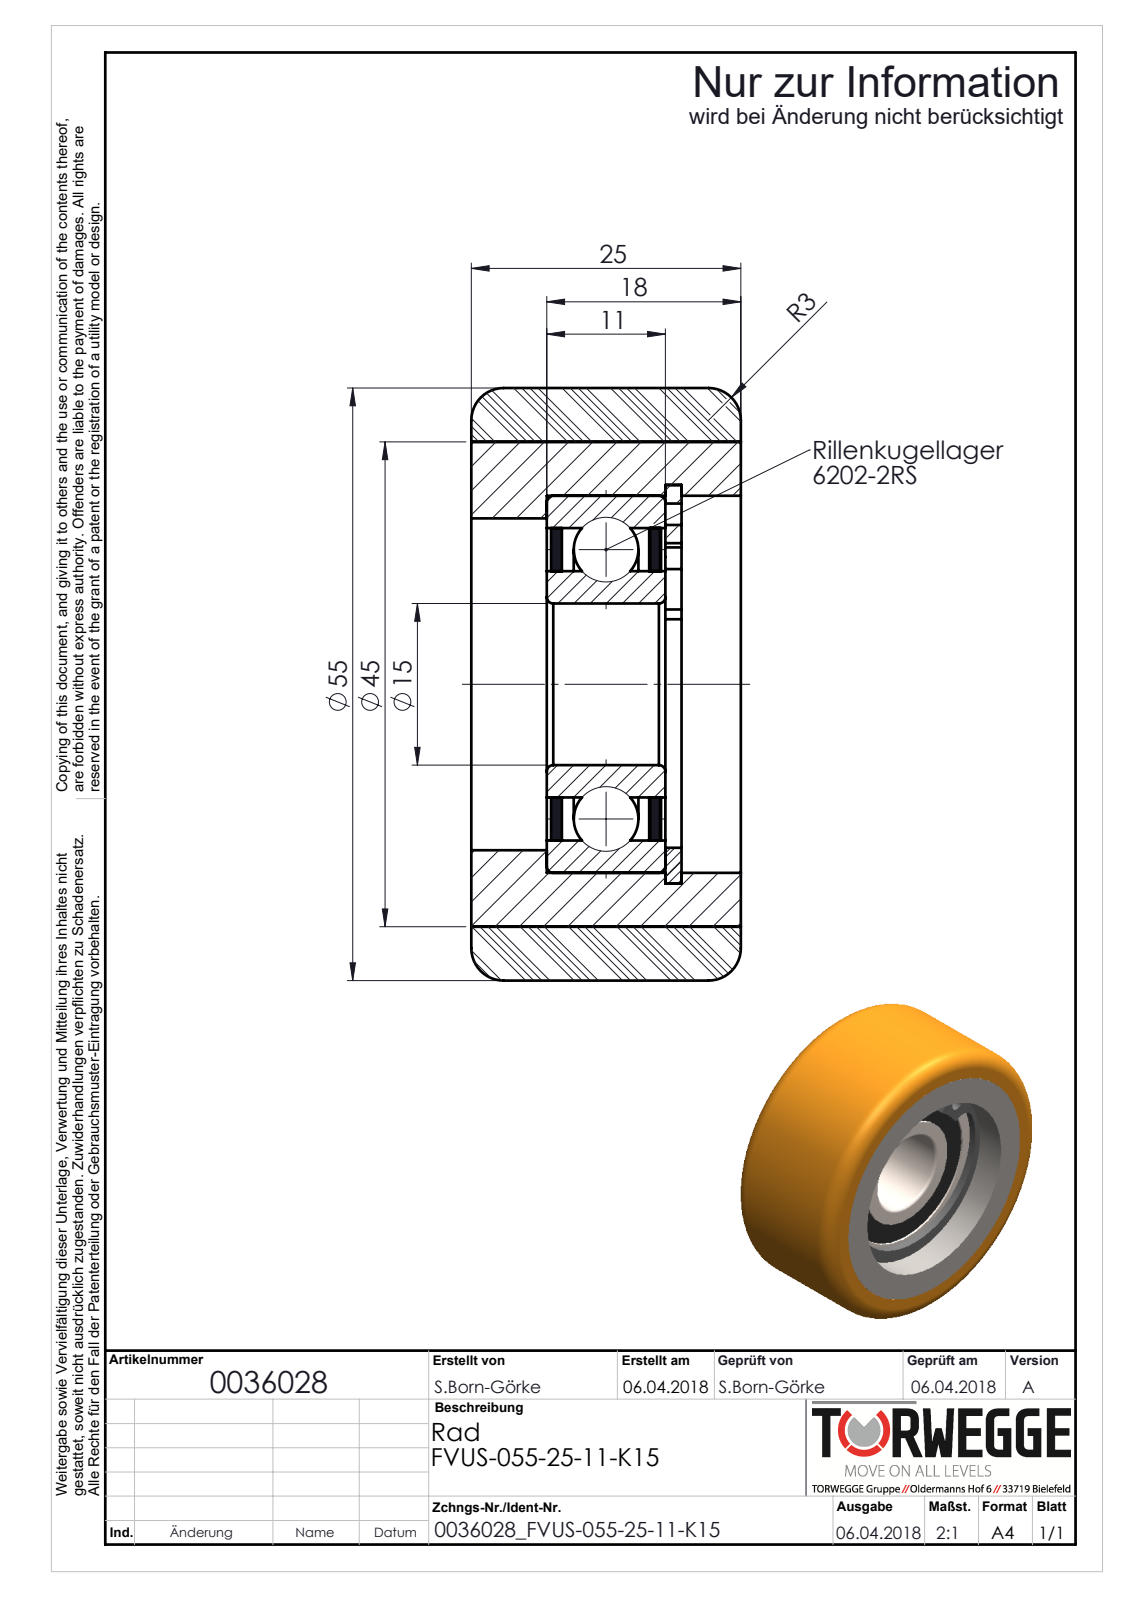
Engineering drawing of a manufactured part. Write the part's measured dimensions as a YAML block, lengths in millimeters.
part_name: "0036028_FVUS-055-25-11-K15"
step_written_by: "SolidWorks 2018 (AUTOMOTIVE_DESIGN)"
units: millimeters
bodies: {solids: 0, faces: 40, planar: 16, cylindrical: 19, other: 5}
overall_size: [55, 55, 25]
round_holes:
  - {diameter: 2.5, count: 2}
  - {diameter: 15, count: 1}
  - {diameter: 29, count: 1}
  - {diameter: 30.8, count: 1}
  - {diameter: 35, count: 1}
  - {diameter: 37, count: 1}
  - {diameter: 45, count: 1}
round_bosses_or_shafts:
  - {diameter: 55, count: 1}
  - {diameter: 21, count: 1}
partial_cylinders:
  - {radius: 2.5, count: 2}
  - {radius: 13.1, count: 1}
  - {radius: 15.95, count: 1}
face_to_face_distances: [25, 7, 18, 7.5, 17.5, 0.5, 10.5, 11, 10, 19.5]
hole_center_spacings: [15.8, 11.81]
